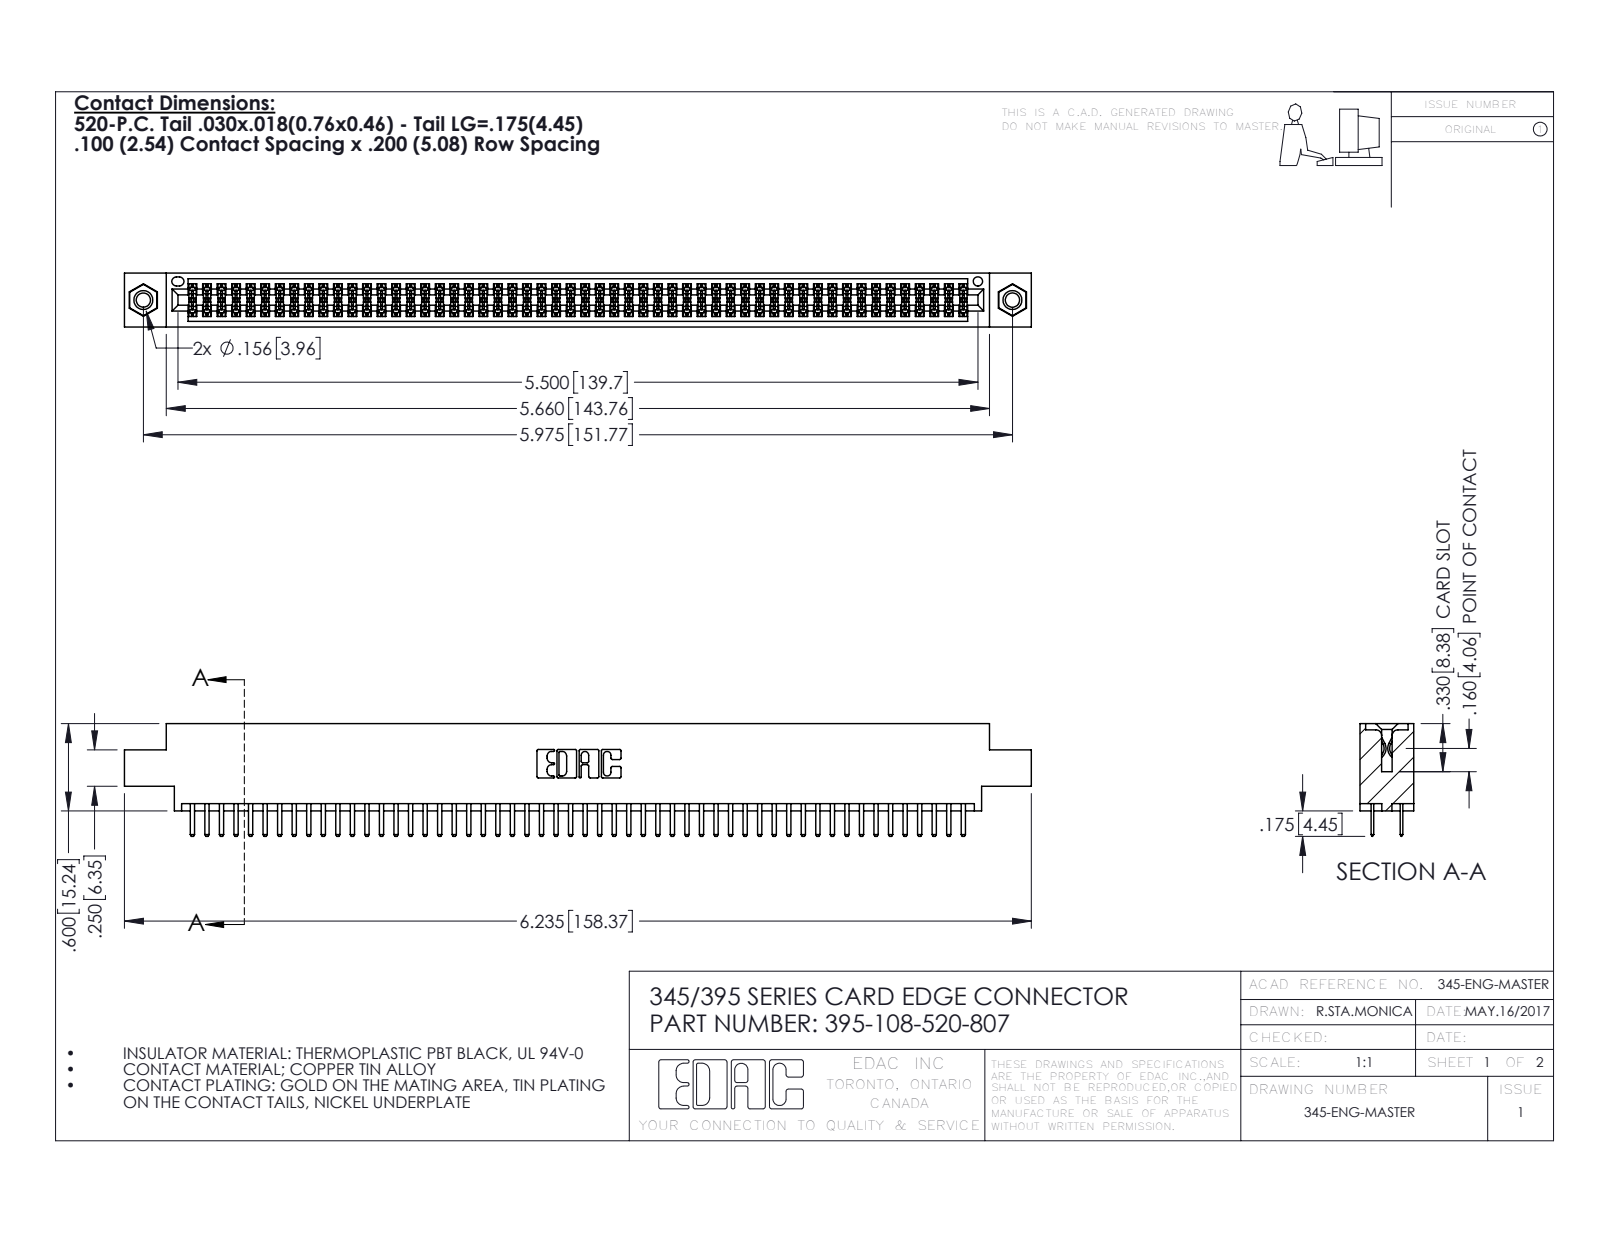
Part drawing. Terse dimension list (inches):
name: 345 Part_0.170 Offset - 0.156 Dia-TI; 345-250-001_345-250-005-103; 395-108-520-807; 345-292-001_345-293-120
written by: SolidWorks 2016 (CONFIG_CONTROL_DESIGN)
unit: in
bodies: 111 solids, 6022 faces (3896 planar, 2110 cylindrical, 16 other)
size: 6.235 × 0.775 × 0.37
volume: 0.935 in³; area: 35.57 in²
holes: 2× ⌀0.098, 2× ⌀0.125, 2× ⌀0.156, 1× ⌀0.064
bosses: 2× ⌀0.155
rounds: 162× R0.006, 112× R0.01, 22× R0.01, 6× R0.007, 6× R0.031, 3× R0.026, 2× R0.014, 2× R0.019
face distances: 0.072, 0.298, 0.2, 0.37, 0.098, 0.272, 0.025, 0.225, 0.022, 0.072
hole spacings: 0.27, 5.739, 5.975
